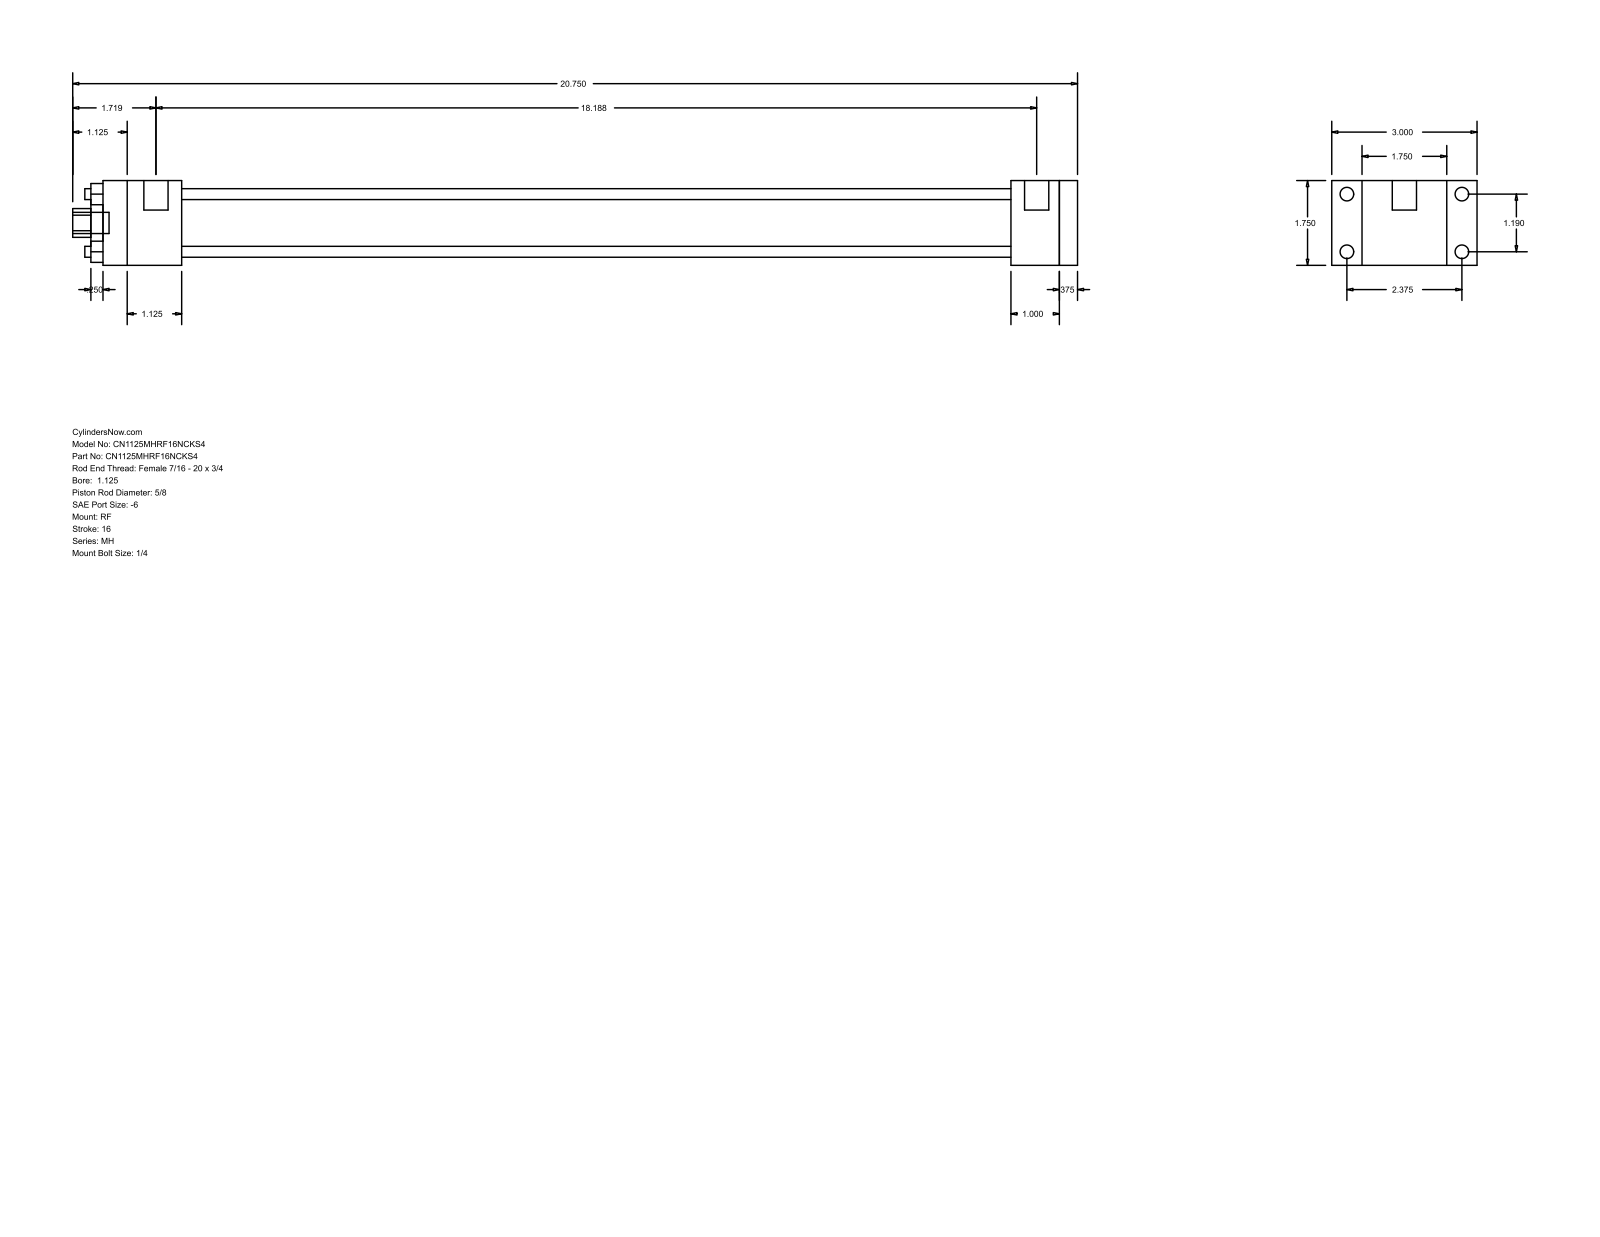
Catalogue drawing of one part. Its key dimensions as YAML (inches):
part_name: "MH_RF__0112_0.625"
step_written_by: "GSSL Pune (CONFIG_CONTROL_DESIGN)"
units: inches
bodies: {solids: 0, faces: 92, planar: 64, cylindrical: 28, other: 0}
overall_size: [20.75, 3, 1.75]
round_holes:
  - {diameter: 0.225, count: 4}
  - {diameter: 0.625, count: 1}
  - {diameter: 1.125, count: 1}
  - {diameter: 1.375, count: 1}
round_bosses_or_shafts:
  - {diameter: 0.281, count: 4}
  - {diameter: 0.219, count: 4}
  - {diameter: 0.5, count: 2}
  - {diameter: 0.437, count: 1}
partial_cylinders:
  - {radius: 0.297, count: 1}
face_to_face_distances: [1.75, 0.375, 20.125, 0.625, 18.125, 18.5, 17.125, 1, 1.375, 1.625]
hole_center_spacings: [0.841, 1.19, 1.683]
